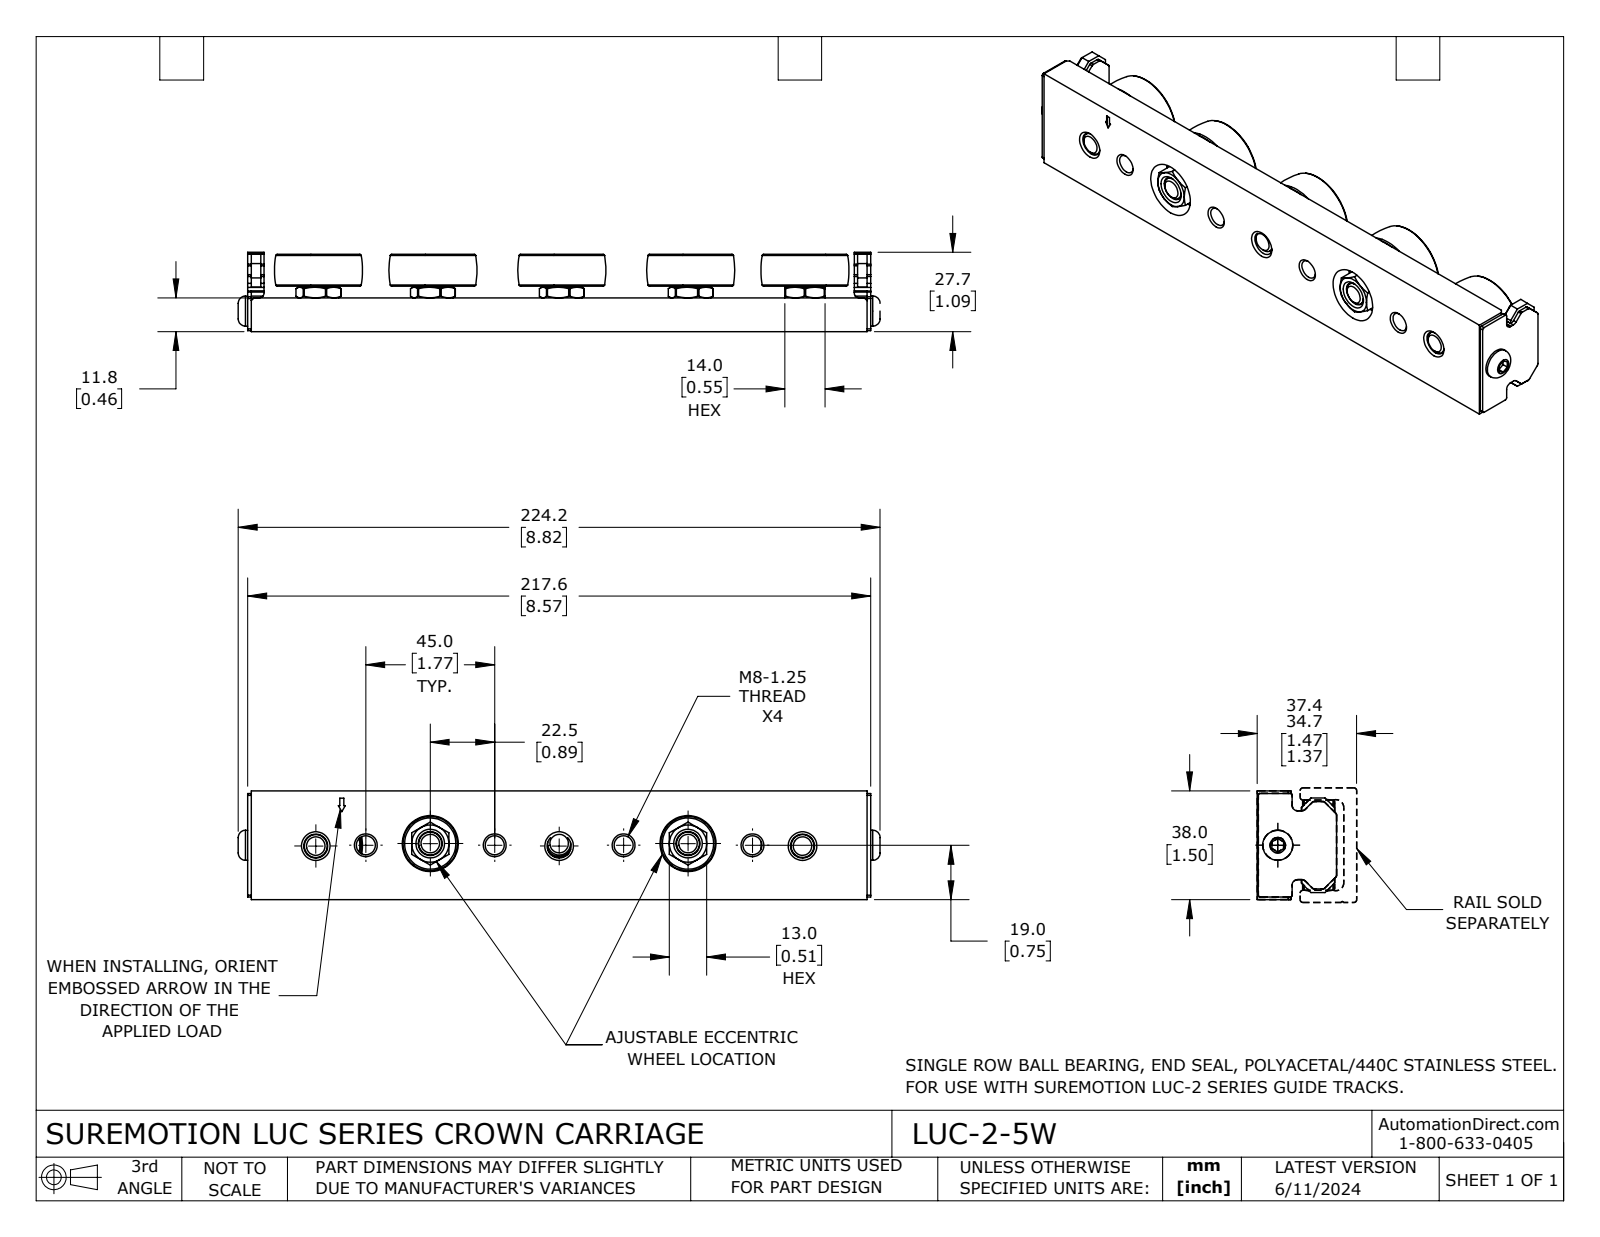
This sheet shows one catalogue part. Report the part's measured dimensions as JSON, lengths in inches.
{"part_name": "LUC-2-5W", "step_written_by": "SolidWorks 2023 (CONFIG_CONTROL_DESIGN)", "units": "inches", "bodies": {"solids": 10, "faces": 736, "planar": 290, "cylindrical": 200, "other": 246}, "overall_size": [8.825, 1.496, 1.09], "volume_in3": 8.351, "surface_area_in2": 75.71, "round_holes": [[0.33, 5], [0.748, 5], [0.262, 4], [0.377, 2], [0.77, 2], [0.194, 1], [0.194, 1]], "round_bosses_or_shafts": [[0.367, 5], [0.315, 5], [0.248, 5], [0.375, 3], [0.375, 2], [0.705, 1], [0.705, 1], [0.413, 1]], "partial_cylinders_radius": [[0.025, 12], [0.015, 6], [0.033, 6], [0.313, 5], [0.078, 4], [0.07, 2]], "face_to_face_distances": [0.464, 1.496, 0.073, 0.365, 0.16, 1.062, 0.598, 0.624, 0.438, 0.05], "hole_center_spacings": [1.772, 0.038, 0.886, 3.544, 0.849, 0.887, 0.924, 1.574]}
